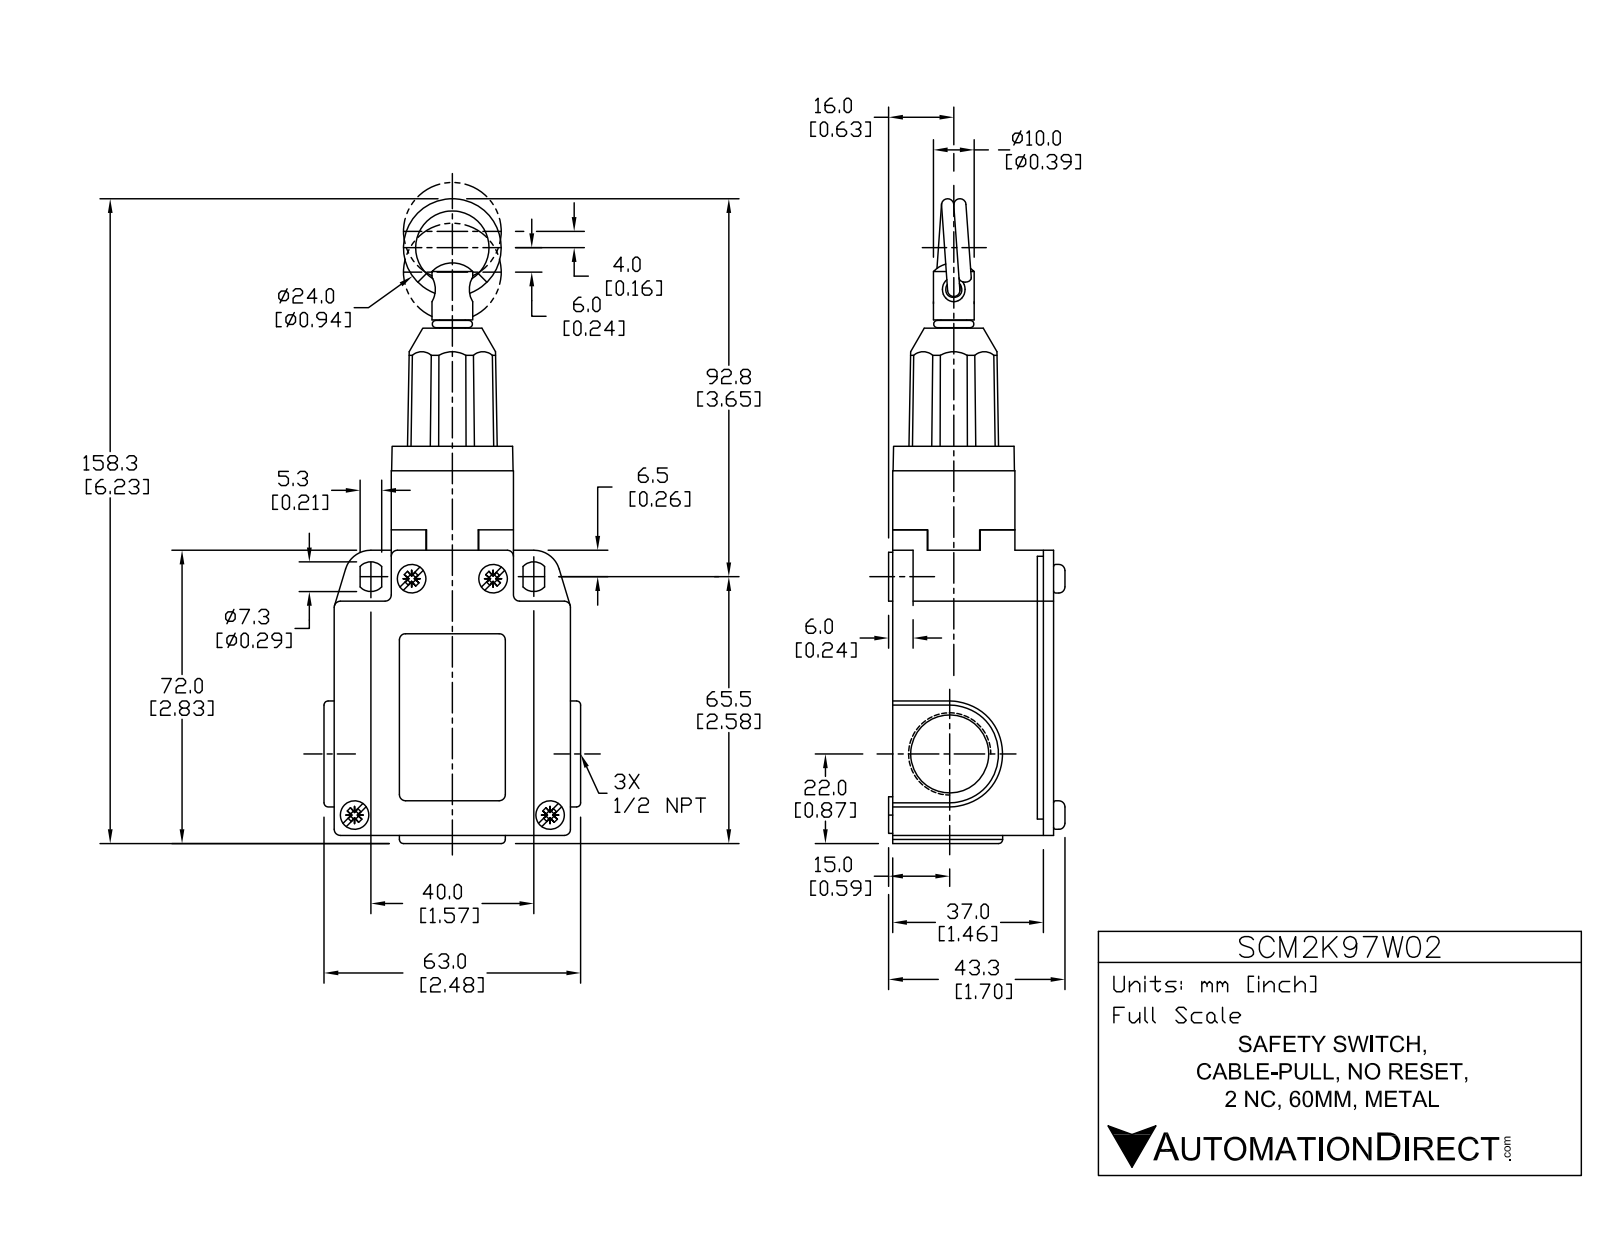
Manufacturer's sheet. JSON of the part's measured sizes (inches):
{"part_name": "SCM2K97W02", "step_written_by": "SolidWorks 2017 (AUTOMOTIVE_DESIGN)", "units": "inches", "bodies": {"solids": 5, "faces": 202, "planar": 89, "cylindrical": 88, "other": 25}, "overall_size": [6.28, 2.441, 1.705], "volume_in3": 10.97, "surface_area_in2": 48.85, "round_holes": [[0.669, 2], [0.748, 2], [0.157, 1], [0.398, 1], [0.709, 1]], "round_bosses_or_shafts": [[0.276, 4], [0.472, 2], [0.354, 2], [0.701, 1], [0.394, 1], [0.248, 1]], "partial_cylinders_radius": [[0.059, 12], [0.144, 2], [0.256, 2], [0.512, 2], [0.453, 1], [0.472, 1]], "face_to_face_distances": [1.555, 0.551, 1.732, 1.181, 2.283, 0.079, 0.236, 0.157, 0.197, 2.756], "hole_center_spacings": [0.039, 4.528]}
